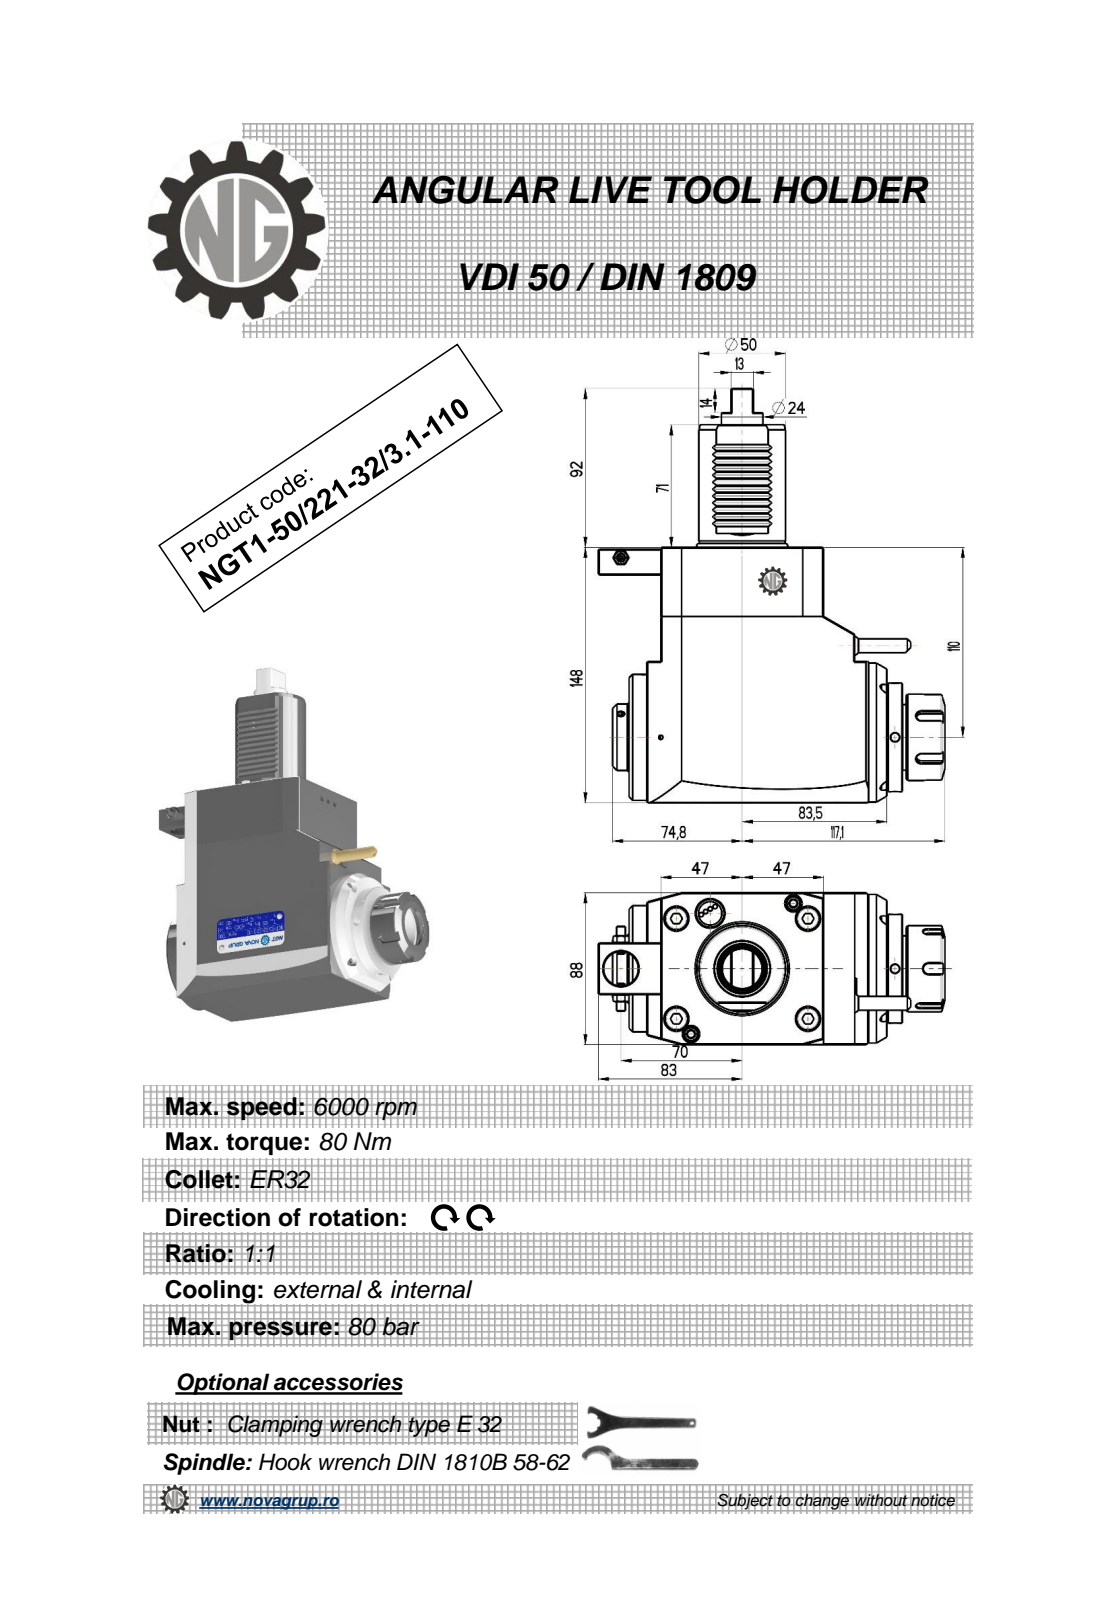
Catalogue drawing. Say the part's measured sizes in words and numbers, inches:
The part is named "NGT1_50_221_32_3_1_110". Its 3-D file was written by "PRO/ENGINEER BY PARAMETRIC TECHNOLOGY CORPORATION, 2010280 (CONFIG_CONTROL_DESIGN)". It is 1 solid with 403 faces: 194 planar, 90 cylindrical and 119 other. Overall it measures 9.449 by 7.878 by 3.465 inches. Its volume is 110.9 cubic inches and its surface area 175.5 square inches. Round holes: 3 of diameter 0.197, 1 of diameter 0.118, 1 of diameter 0.374, 1 of diameter 0.787, 1 of diameter 1.063. Round bosses or shafts: 2 of diameter 1.969, 1 of diameter 3.386, 1 of diameter 2.874, 1 of diameter 2.48, 1 of diameter 1.988, 1 of diameter 1.614, 1 of diameter 1.575, 1 of diameter 1.516. Partial cylindrical surfaces (rounded edges, fillets, slot ends): 12 of radius 0.01, 12 of radius 0.012, 6 of radius 0.008, 5 of radius 0.118, 2 of radius 0.031. The main face-to-face distances are 3.465, 5.827, 0.315, 3.701, 0.72, 5.138, 1.437, 4.724, 4.421, 5.858. The hole center spacings are 2.065, 2.23, 3.996, 6.23.
